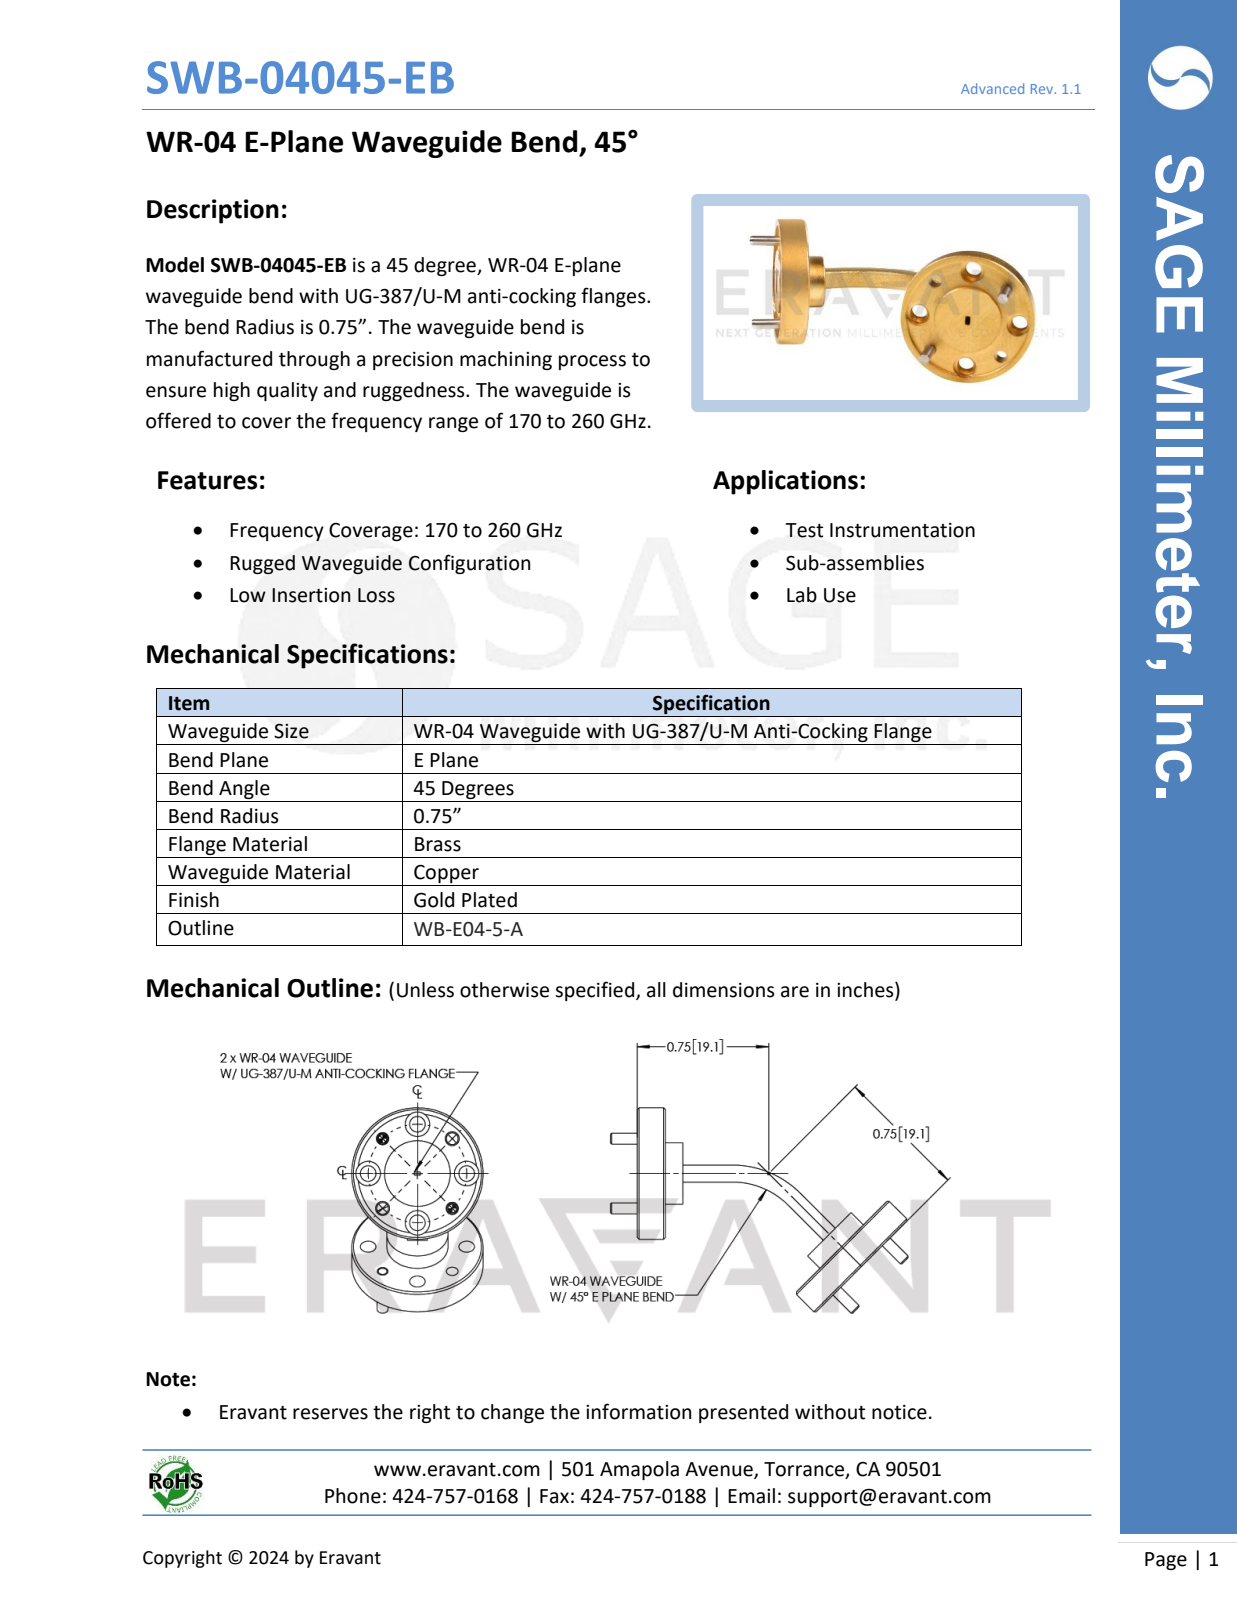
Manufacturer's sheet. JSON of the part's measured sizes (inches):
{"part_name": "WB-H04-5-A, defeatured_02", "step_written_by": "SolidWorks 2021 (AUTOMOTIVE_DESIGN)", "units": "inches", "bodies": {"solids": 5, "faces": 158, "planar": 38, "cylindrical": 80, "other": 40}, "overall_size": [1.699, 1.171, 0.75], "volume_in3": 0.149, "surface_area_in2": 4.119, "round_holes": [[0.089, 8], [0.14, 8], [0.061, 4], [0.067, 4], [0.68, 2]], "round_bosses_or_shafts": [[0.063, 4], [0.75, 2], [0.35, 2], [0.375, 1], [0.375, 1]], "partial_cylinders_radius": [[0.449, 1], [0.489, 1], [0.511, 1], [0.551, 1]], "face_to_face_distances": [0.16, 0.1, 0.14, 0.13, 0.26, 0.03, 0.02, 0.04, 0.123, 0.061], "hole_center_spacings": [0.215, 0.281, 0.398, 0.52, 0.519, 0.562, 0.281, 0.398]}
